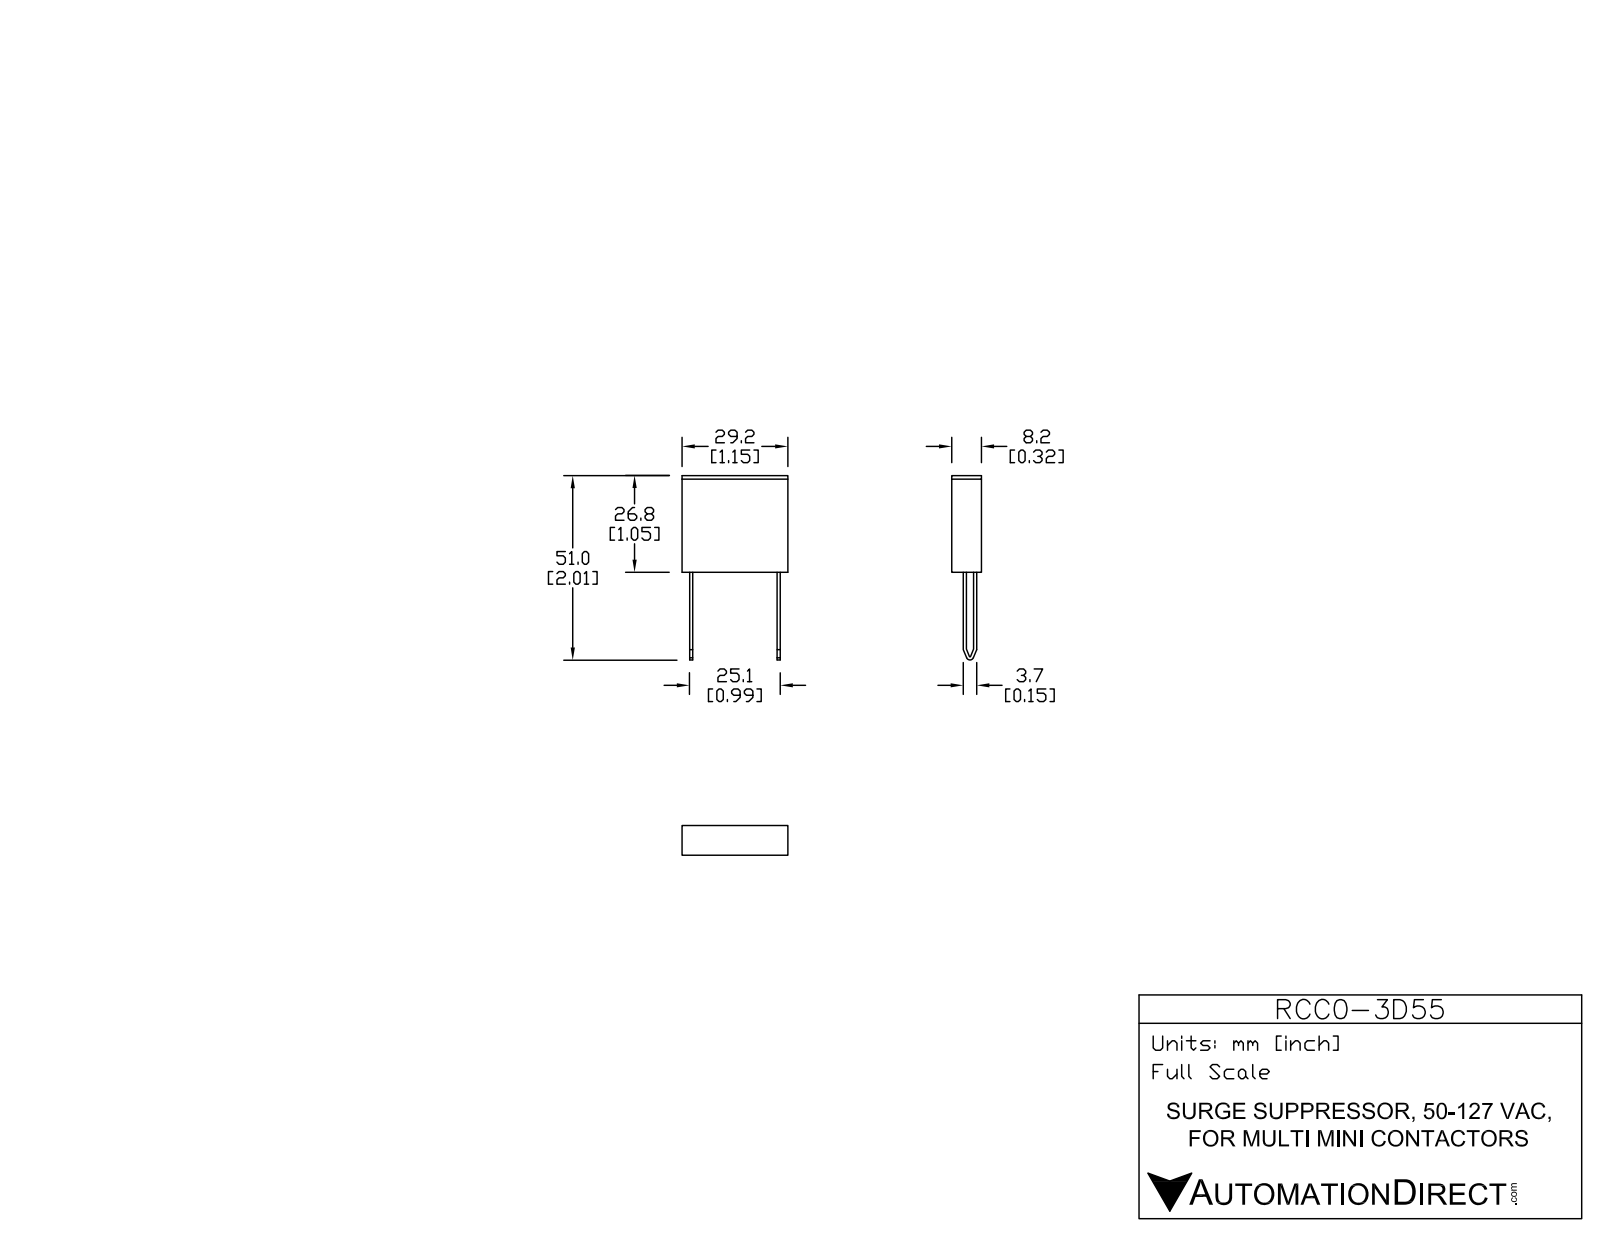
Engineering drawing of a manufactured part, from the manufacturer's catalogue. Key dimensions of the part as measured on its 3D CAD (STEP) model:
Part name (STEP PRODUCT): RCC0-3D55
STEP written by: SolidWorks 2013 (AUTOMOTIVE_DESIGN)
Units: millimetres
Bodies: 1 solid, 34 faces (26 planar, 8 cylindrical, 0 other)
Overall size (bounding box): 50.9 × 29.2 × 8.2
Volume: 6 463 mm³ · Surface area: 2 803 mm²
Partial cylindrical surfaces — rounded edges, fillets, slot ends (radius × count): R0.15 ×1, R1 ×1
Main face-to-face distances: 8.2, 26.7, 29.2, 0.85, 2.1, 27.1, 2.95, 26.25, 24.15, 2.85
